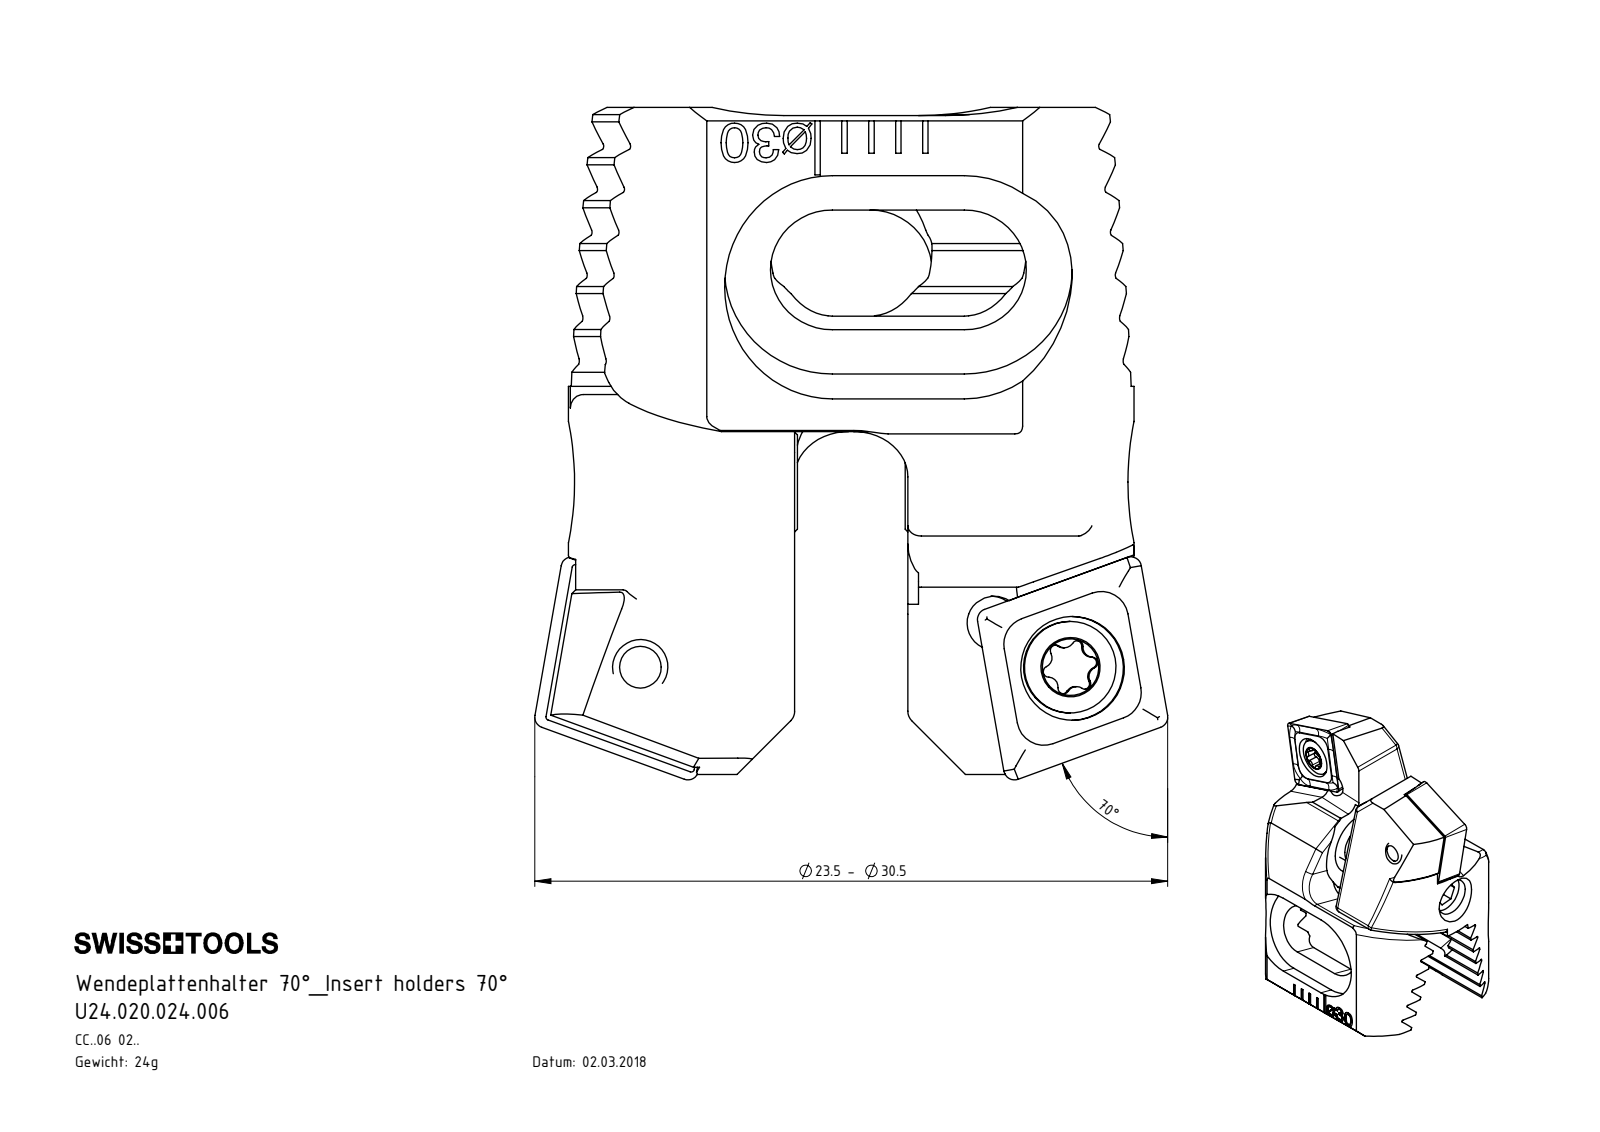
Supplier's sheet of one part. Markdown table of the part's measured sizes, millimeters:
| quantity | value |
| --- | --- |
| part name | Z20-xxx.001.015_D_70ø; CCMT060204; Z20.WCA.B70.015; WCA-ER2.001.006_A (+1 more) |
| STEP written by | SolidWorks 2017 (AUTOMOTIVE_DESIGN) |
| units | millimeters |
| bodies | 8 solids, 542 faces (266 planar, 106 cylindrical, 170 other) |
| overall size | 24.95 × 23.5 × 16.2 |
| volume | 2 926 mm³ |
| surface area | 3 395 mm² |
| round holes (diameter × count) | 1.6 × 2, 2 × 2, 2.05 × 2, 2.8 × 2, 3.85 × 2, 3.5 × 1, 9.1 × 1 |
| round bosses / shafts (diameter × count) | 3.4 × 2, 2.5 × 2, 4 × 1 |
| partial cylindrical surfaces (radius × count) | 0.5 × 16, 0.12 × 12, 0.21 × 12, 0.36 × 10, 1 × 6, 2 × 4, 2.3 × 4, 4 × 4 |
| main face-to-face distances | 1.43, 2.86, 4.29, 3.79, 0.4, 4.6, 5.71, 5.72, 2.97, 6.76 |
| hole center spacings | 3.27, 3.36, 5.5, 13.51, 13.59, 16.32, 10.57, 10.62 |
